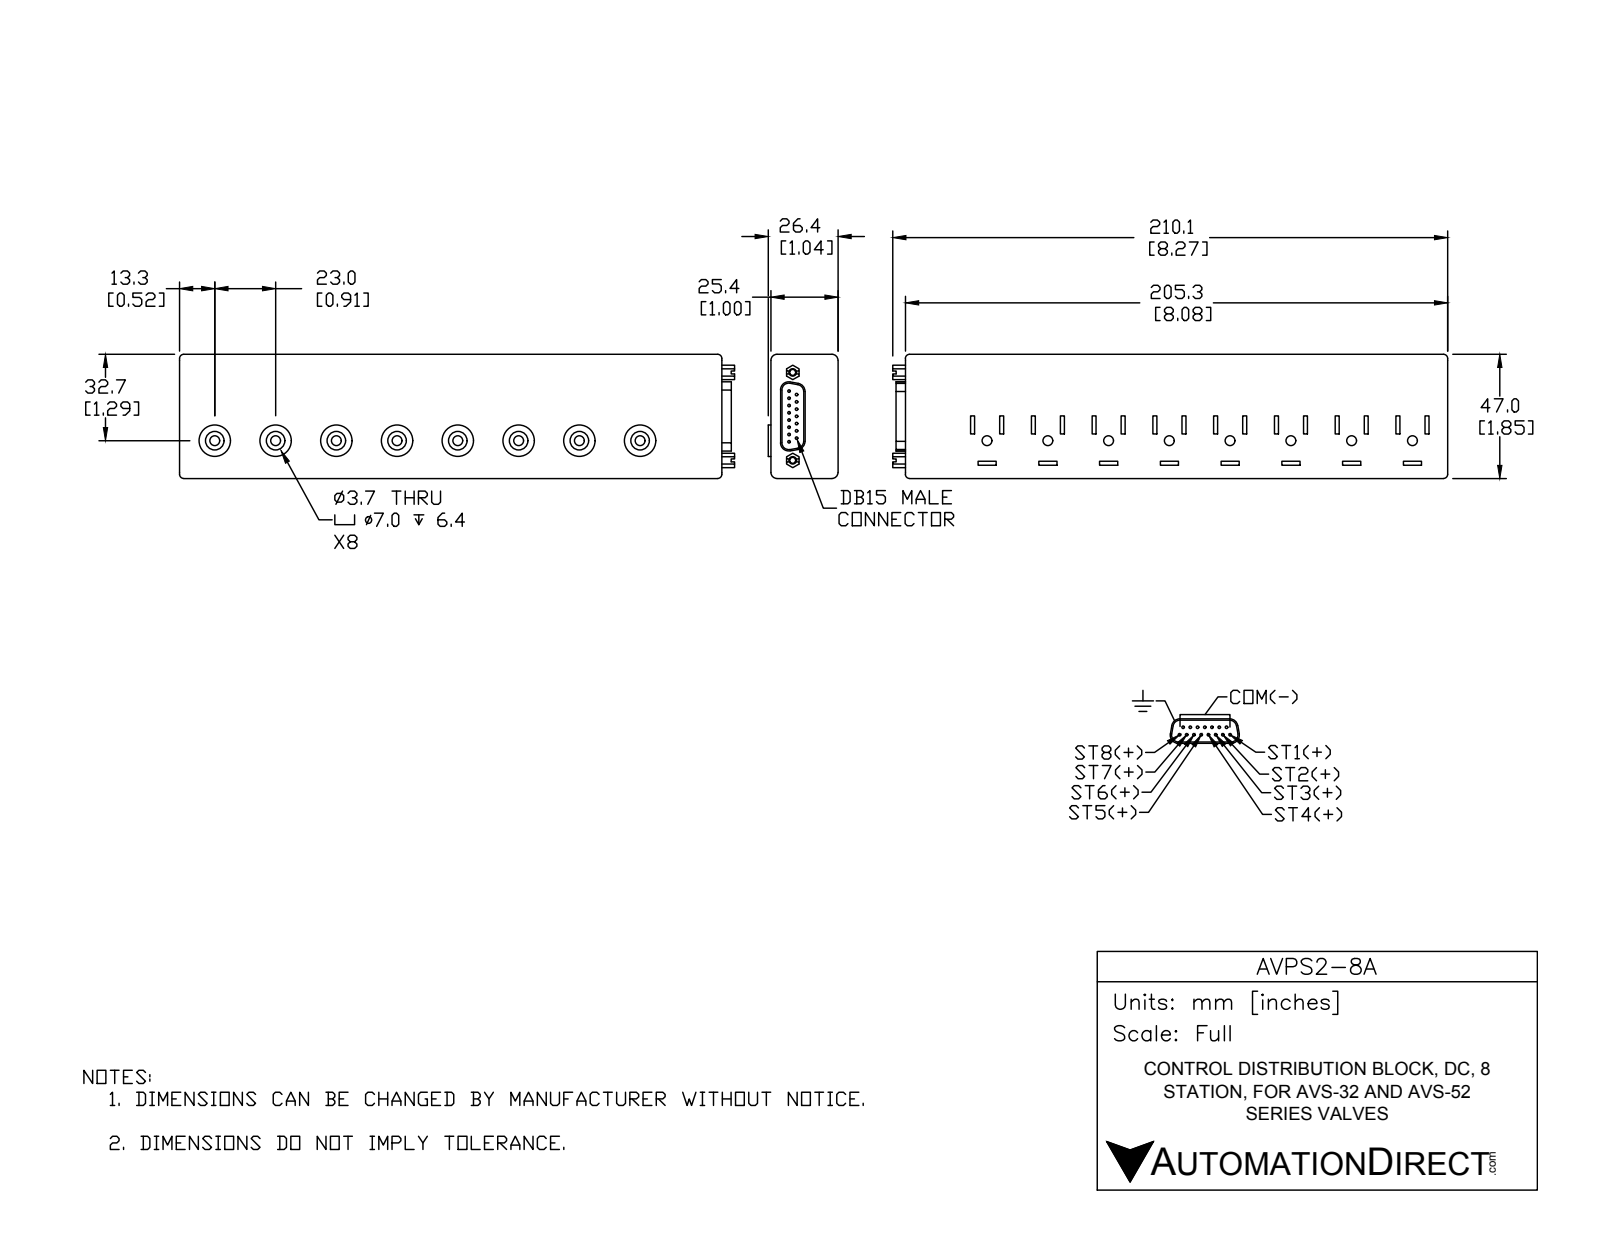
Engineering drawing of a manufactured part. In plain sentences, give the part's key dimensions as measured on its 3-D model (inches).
The part is named "AVPS2-8A". Its 3-D file was written by "SolidWorks 2016 (AUTOMOTIVE_DESIGN)". It is 1 solid with 311 faces: 195 planar, 104 cylindrical and 12 other. Overall it measures 8.273 by 1.85 by 1.04 inches. Its volume is 14.61 cubic inches and its surface area 58.73 square inches. Round holes: 8 of diameter 0.145, 8 of diameter 0.275, 2 of diameter 0.089. Round bosses or shafts: 15 of diameter 0.039, 8 of diameter 0.469. Partial cylindrical surfaces (rounded edges, fillets, slot ends): 8 of radius 0.062, 4 of radius 0.09, 4 of radius 0.102, 4 of radius 0.122. The main face-to-face distances are 1, 1.85, 8.084, 0.04, 1.04, 0.059, 0.25, 0.79, 0.906, 1.812. The hole center spacings are 0.906, 1.812, 2.718, 3.624, 0.906, 1.812, 4.53, 5.436.
